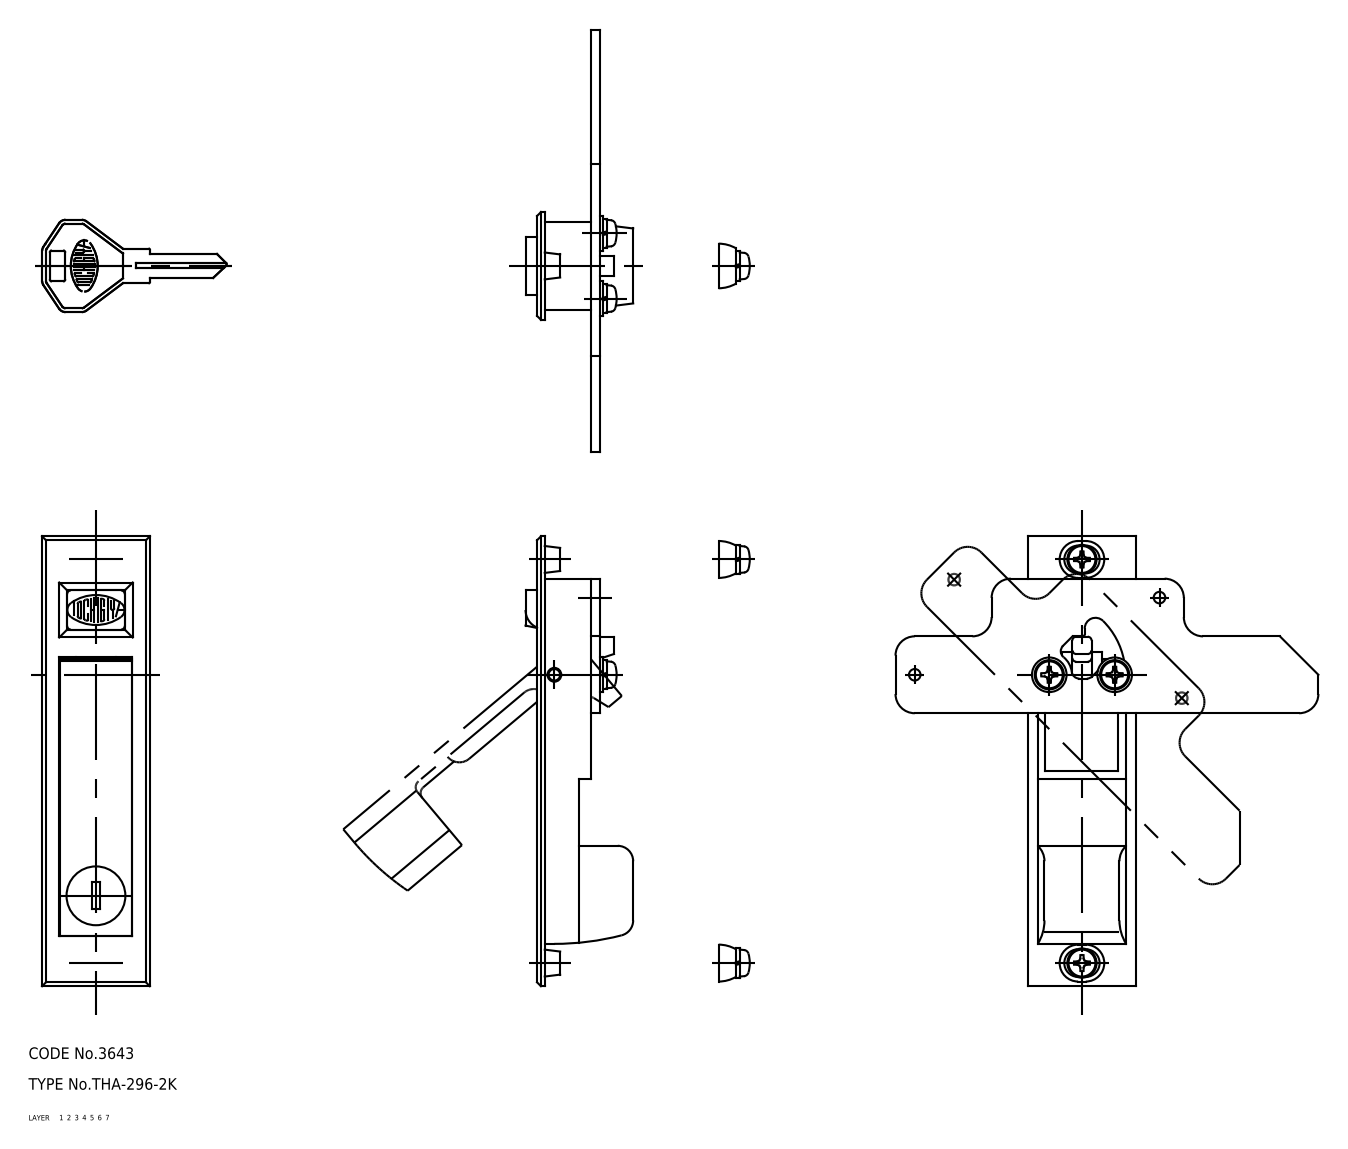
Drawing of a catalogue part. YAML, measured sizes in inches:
part_name: "screw_A; screw_B; bracket; lock (+7 more)"
step_written_by: "CADfix (AUTOMOTIVE_DESIGN)"
units: inches
bodies: {solids: 13, faces: 438, planar: 0, cylindrical: 0, other: 438}
overall_size: [4.606, 4.331, 4.303]
volume: 2.288
surface_area: 51.84
